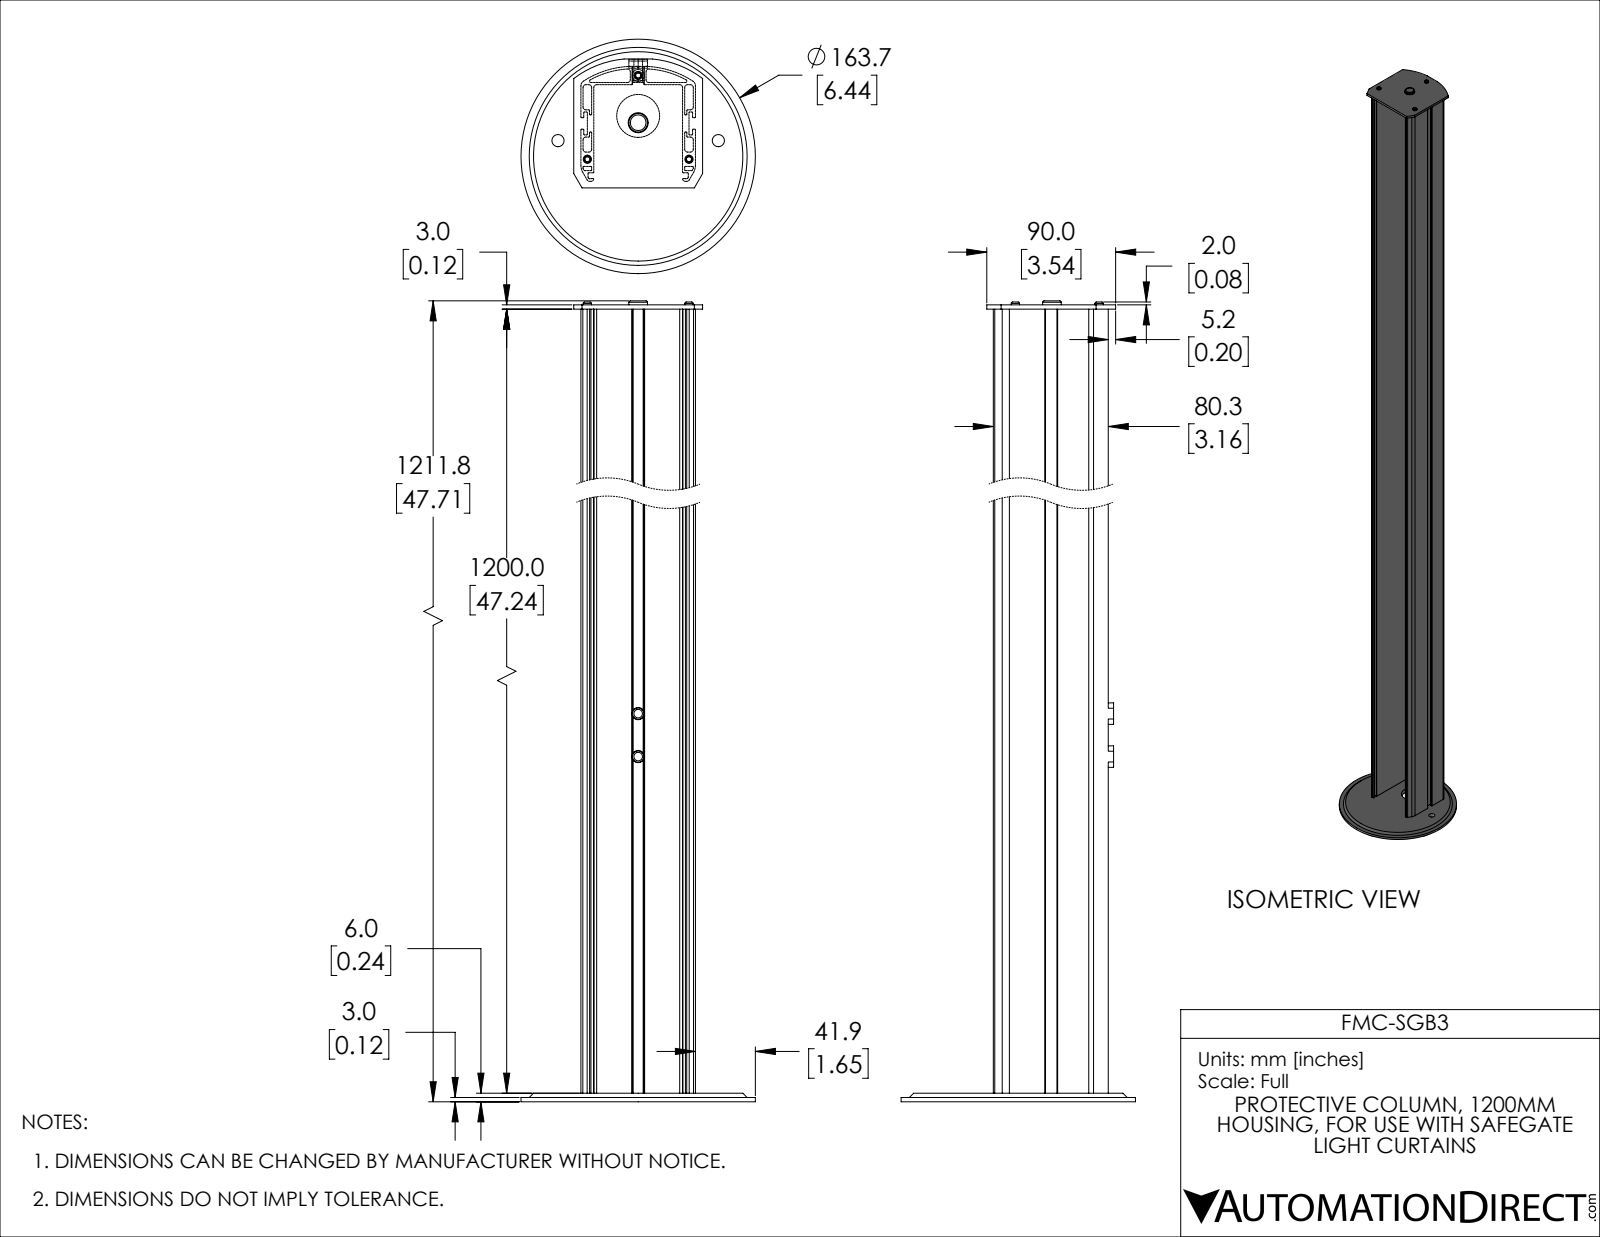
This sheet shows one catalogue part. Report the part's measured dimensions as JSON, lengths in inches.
{"part_name": "FMC-SGB3", "step_written_by": "SolidWorks 2019 (AUTOMOTIVE_DESIGN)", "units": "inches", "bodies": {"solids": 11, "faces": 314, "planar": 161, "cylindrical": 148, "other": 5}, "overall_size": [47.709, 6.445, 6.445], "volume_in3": 77.35, "surface_area_in2": 1738, "round_holes": [[0.335, 7], [0.236, 4], [0.177, 3], [0.197, 3], [0.551, 1], [1.181, 1]], "round_bosses_or_shafts": [[0.315, 4], [0.227, 3], [0.138, 3], [6.445, 1], [0.512, 1]], "partial_cylinders_radius": [[0.02, 59], [0.079, 22], [0.039, 2], [0.157, 2], [0.394, 2], [2.446, 2], [2.5, 2], [2.697, 2]], "face_to_face_distances": [0.059, 2.795, 0.295, 0.354, 0.118, 2.854, 0.177, 0.236, 2.5, 2.441], "hole_center_spacings": [0.956, 1.181, 1.721, 1.836, 2.259, 2.307, 2.694, 2.841]}
